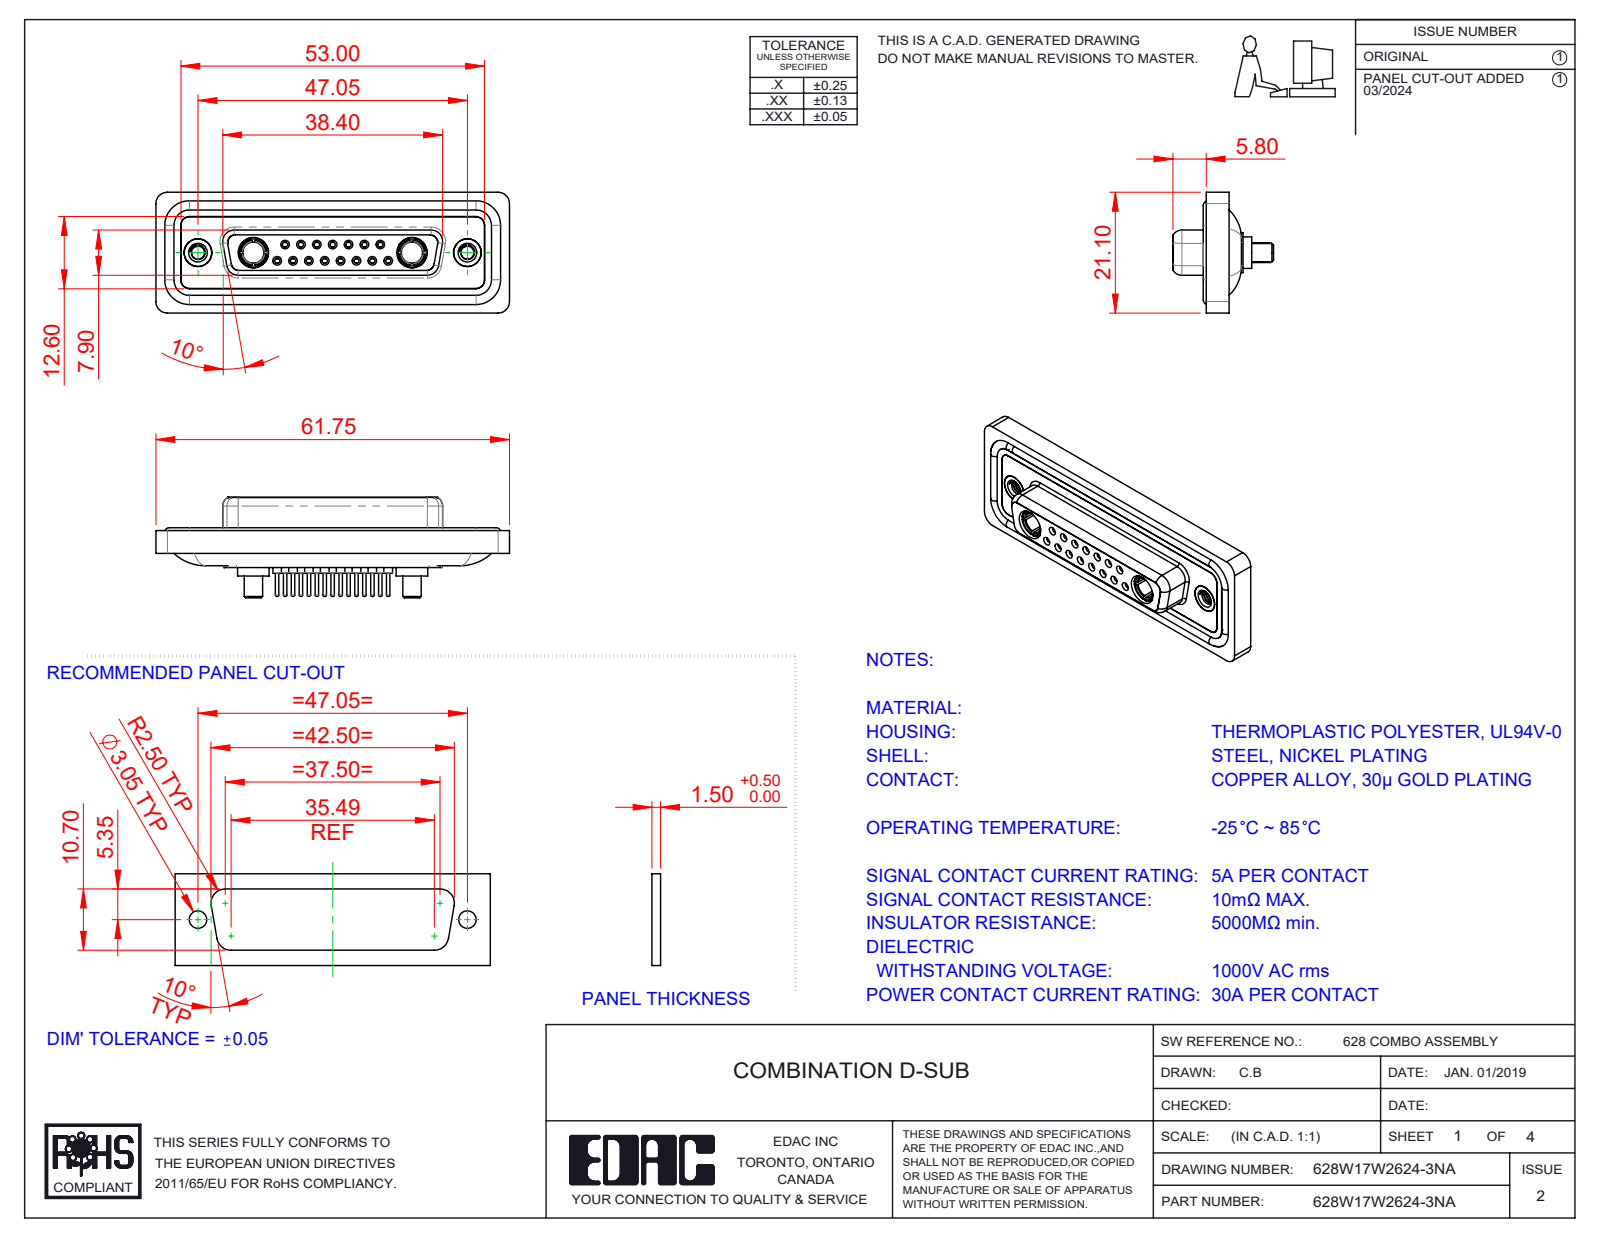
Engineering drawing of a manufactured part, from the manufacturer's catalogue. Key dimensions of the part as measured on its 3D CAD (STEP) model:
Part name (STEP PRODUCT): Power Socket_30A S; 628Combo Contact Row 1_24; 628Combo Shell Front_25 Contacts; 628W17W2624-3NA (+5 more)
STEP written by: SolidWorks 2023 (CONFIG_CONTROL_DESIGN)
Units: millimetres
Bodies: 26 solids, 1357 faces (388 planar, 521 cylindrical, 448 other)
Overall size (bounding box): 61.75 × 21.1 × 17.55
Volume: 8 340 mm³ · Surface area: 13 862 mm²
Round holes (diameter × count): ⌀0.9 ×15, ⌀1.1 ×15, ⌀1.5 ×15, ⌀2 ×15, ⌀1.6 ×8, ⌀1.7 ×7, ⌀4.85 ×4, ⌀2.26 ×2, ⌀3.7 ×2, ⌀4 ×2, ⌀4.05 ×2, ⌀5 ×2
Round bosses / shafts (diameter × count): ⌀2.2 ×15, ⌀0.6 ×15, ⌀1.6 ×11, ⌀5.5 ×2, ⌀5.2 ×2, ⌀4.96 ×2, ⌀4.95 ×2, ⌀4.8 ×2
Partial cylindrical surfaces — rounded edges, fillets, slot ends (radius × count): R1.5 ×22, R2 ×18, R1.35 ×8, R1.6 ×8, R0.25 ×4, R0.5 ×4, R0.6 ×4, R0.65 ×4
Main face-to-face distances: 0.4, 1.8, 7.45, 5.65, 6.6, 0.5, 7.05, 1.6, 2.9, 1.1
Hole centre spacings: 3.16, 2.77, 8.31, 5.54, 5.03, 5.04, 7.49, 11.08
